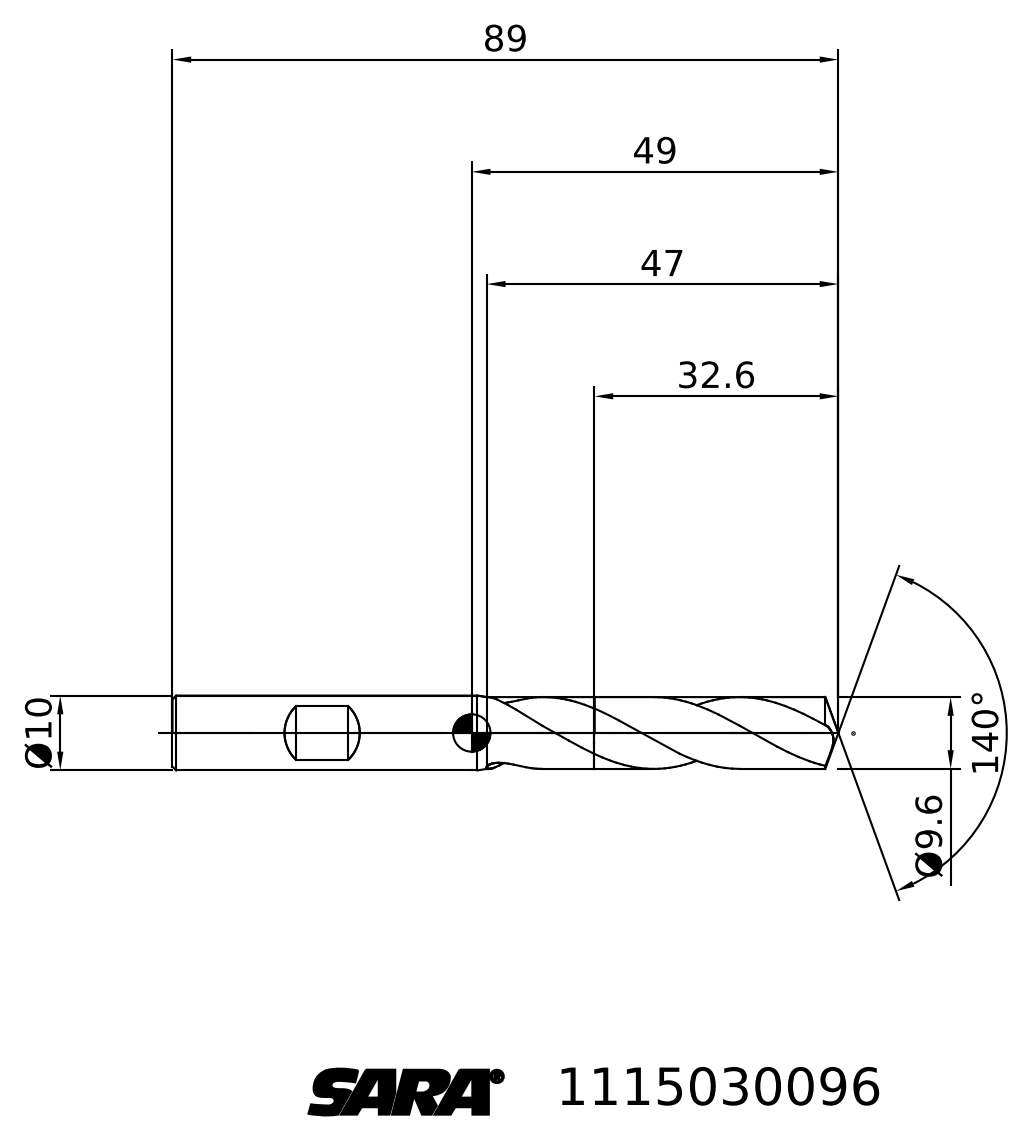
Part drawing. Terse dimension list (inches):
written by: TDM (AUTOMOTIVE_DESIGN)
unit: in
bodies: 2 solids, 30 faces (6 planar, 0 cylindrical, 24 other)
size: 3.504 × 0.394 × 0.394
volume: 0.335 in³; area: 4.693 in²
face distances: 2.22
